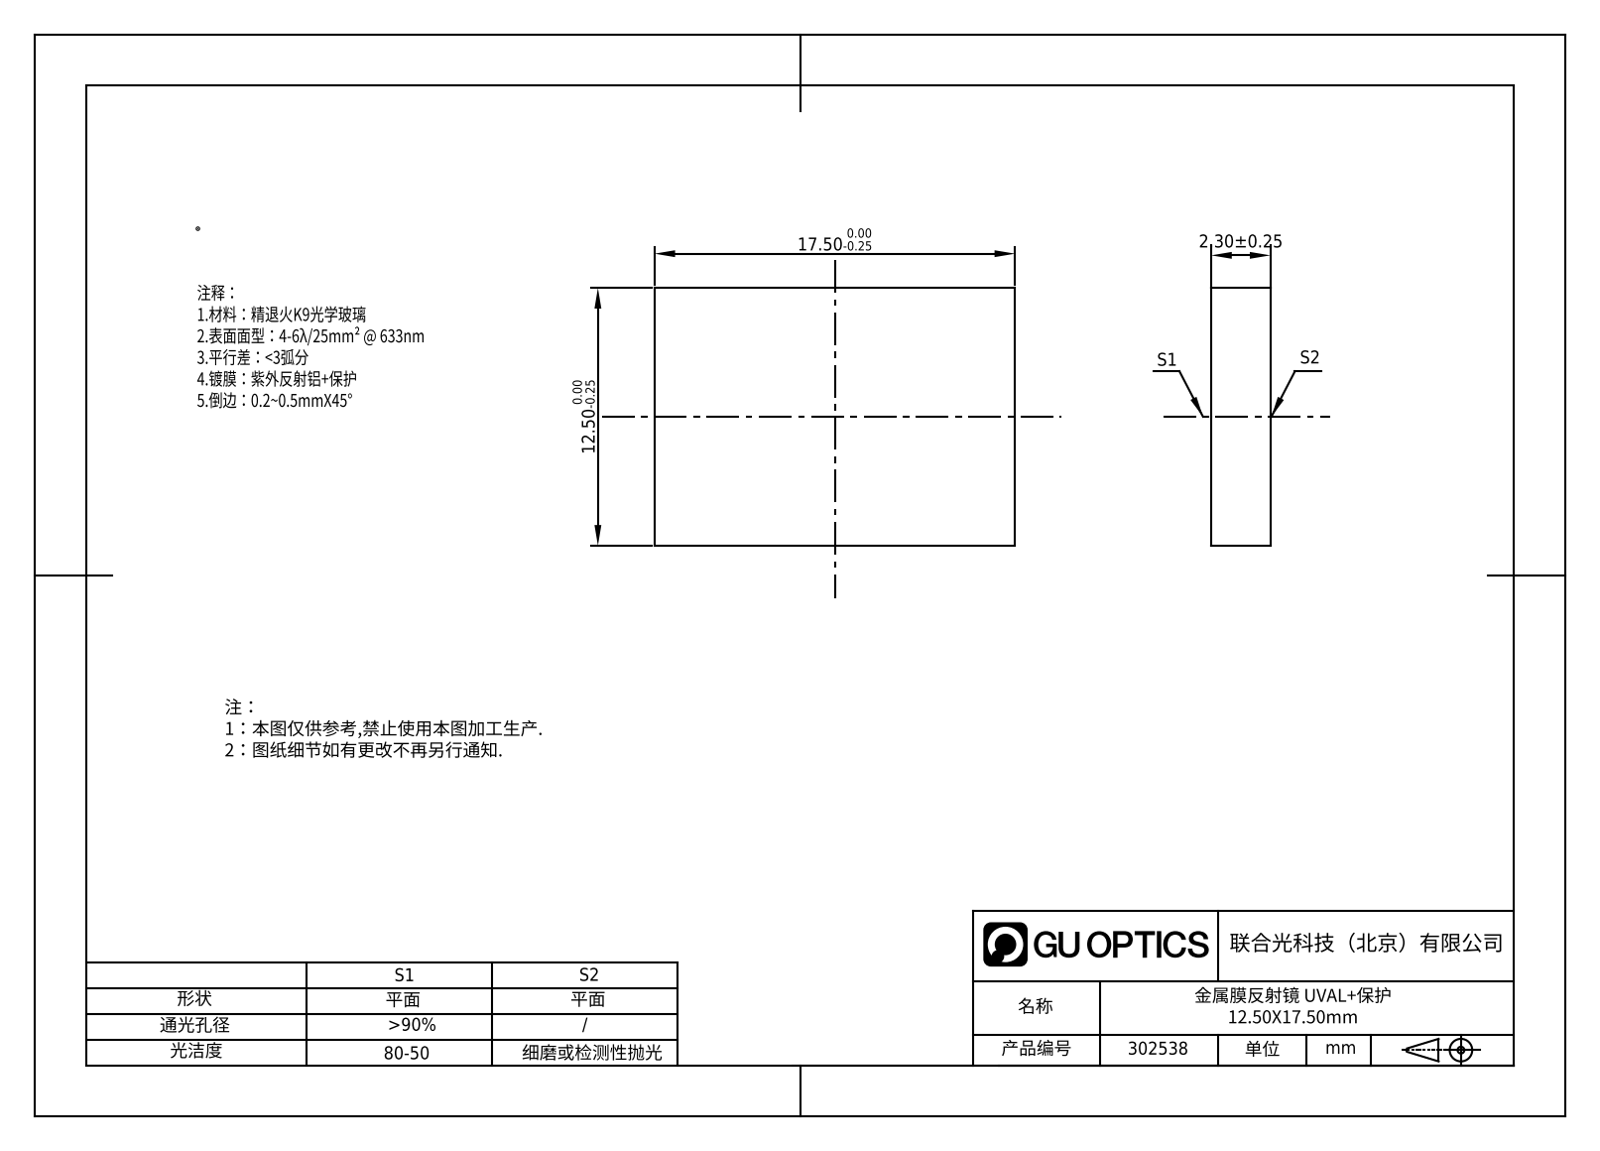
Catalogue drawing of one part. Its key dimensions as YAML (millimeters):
part_name: "302509"
step_written_by: "SolidWorks 2016 (AUTOMOTIVE_DESIGN)"
units: millimeters
bodies: {solids: 1, faces: 6, planar: 6, cylindrical: 0, other: 0}
overall_size: [17.5, 12.5, 2.3]
volume: 503
surface_area: 576
face_to_face_distances: [2.3, 12.5, 17.5]
